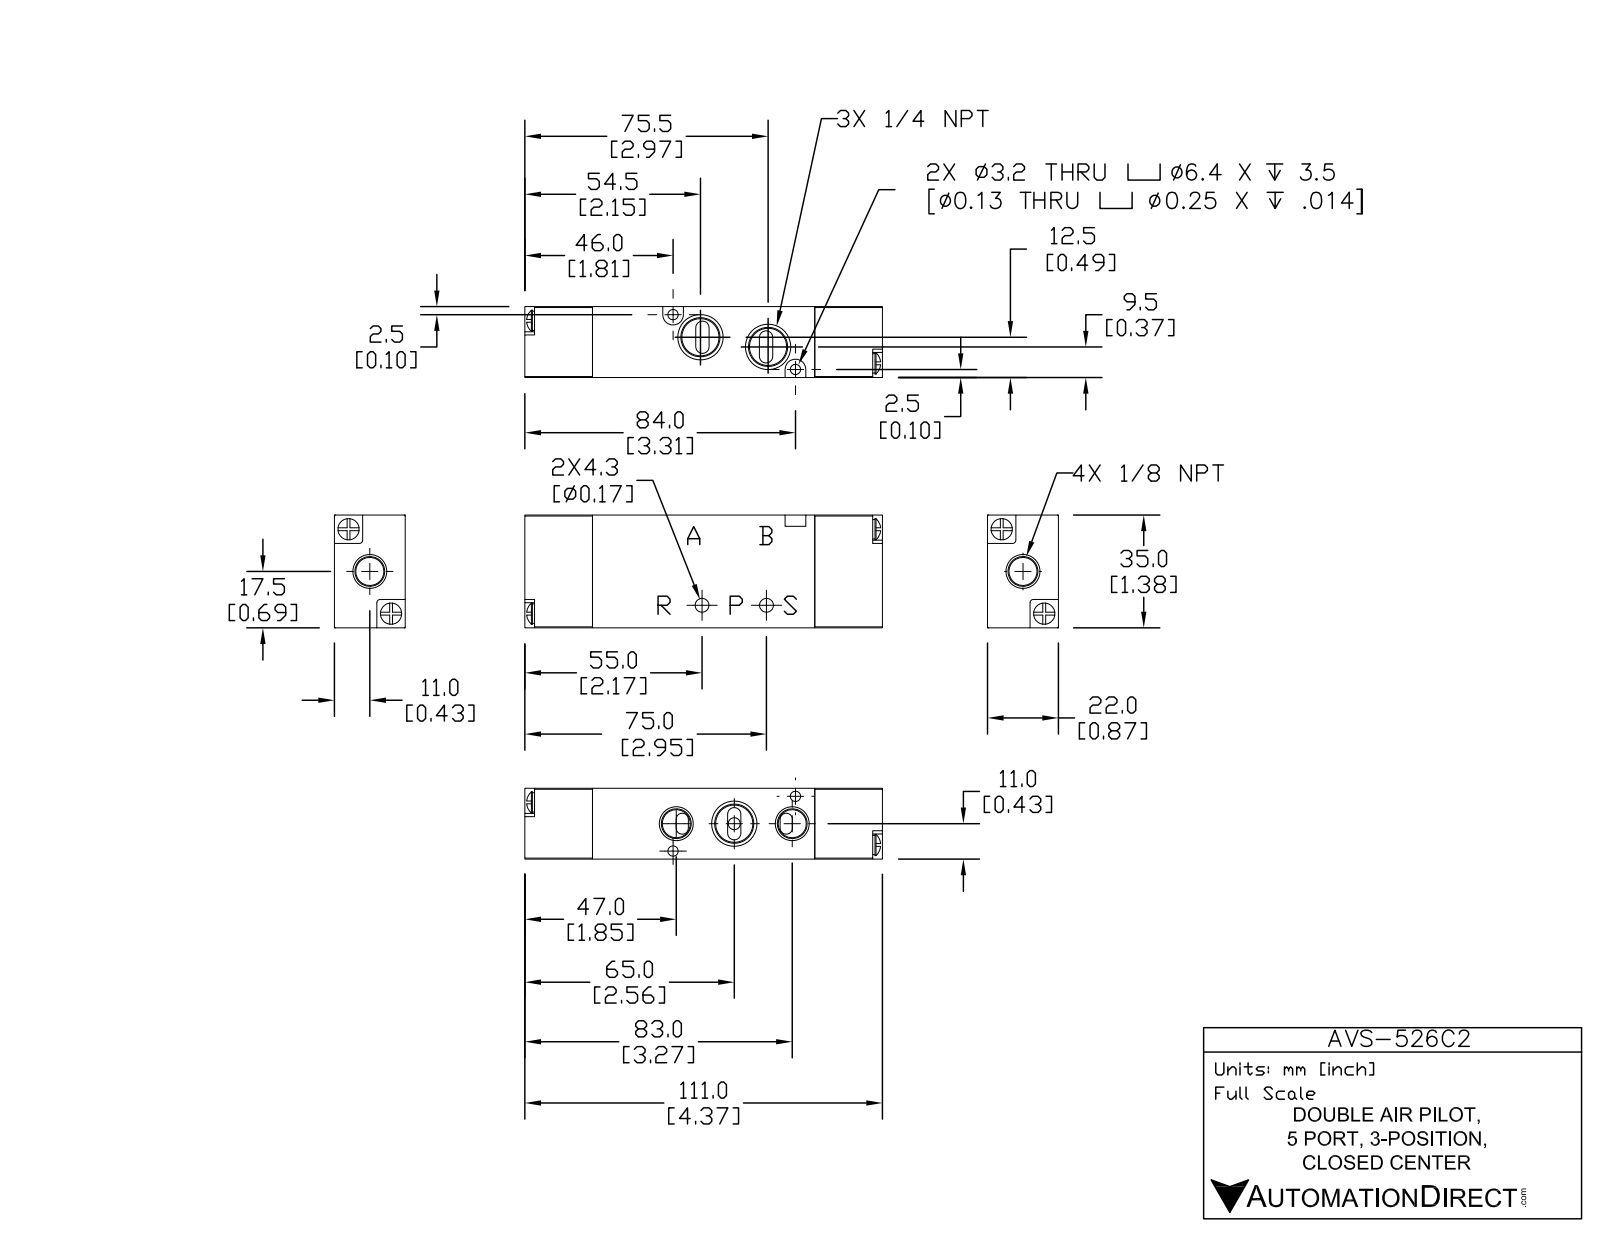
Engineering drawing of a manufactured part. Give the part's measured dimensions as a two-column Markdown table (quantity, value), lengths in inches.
| quantity | value |
| --- | --- |
| part name | AVS-526C2 |
| STEP written by | SolidWorks 2015 (CONFIG_CONTROL_DESIGN) |
| units | inches |
| bodies | 3 solids, 199 faces (99 planar, 56 cylindrical, 44 other) |
| overall size | 4.37 × 1.378 × 0.866 |
| volume | 4.681 in³ |
| surface area | 32.91 in² |
| round holes (diameter × count) | 0.126 × 2, 0.169 × 2, 0.146 × 1 |
| round bosses / shafts (diameter × count) | 0.26 × 4, 0.236 × 4 |
| partial cylindrical surfaces (radius × count) | 0.081 × 6, 0.012 × 4, 0.039 × 4, 0.075 × 4, 0.126 × 2 |
| main face-to-face distances | 0.866, 1.378, 2.717, 0.827, 3.543, 4.37, 0.411, 0.967, 0.551, 0.118 |
| hole center spacings | 0.819, 0.787, 1.639 |
